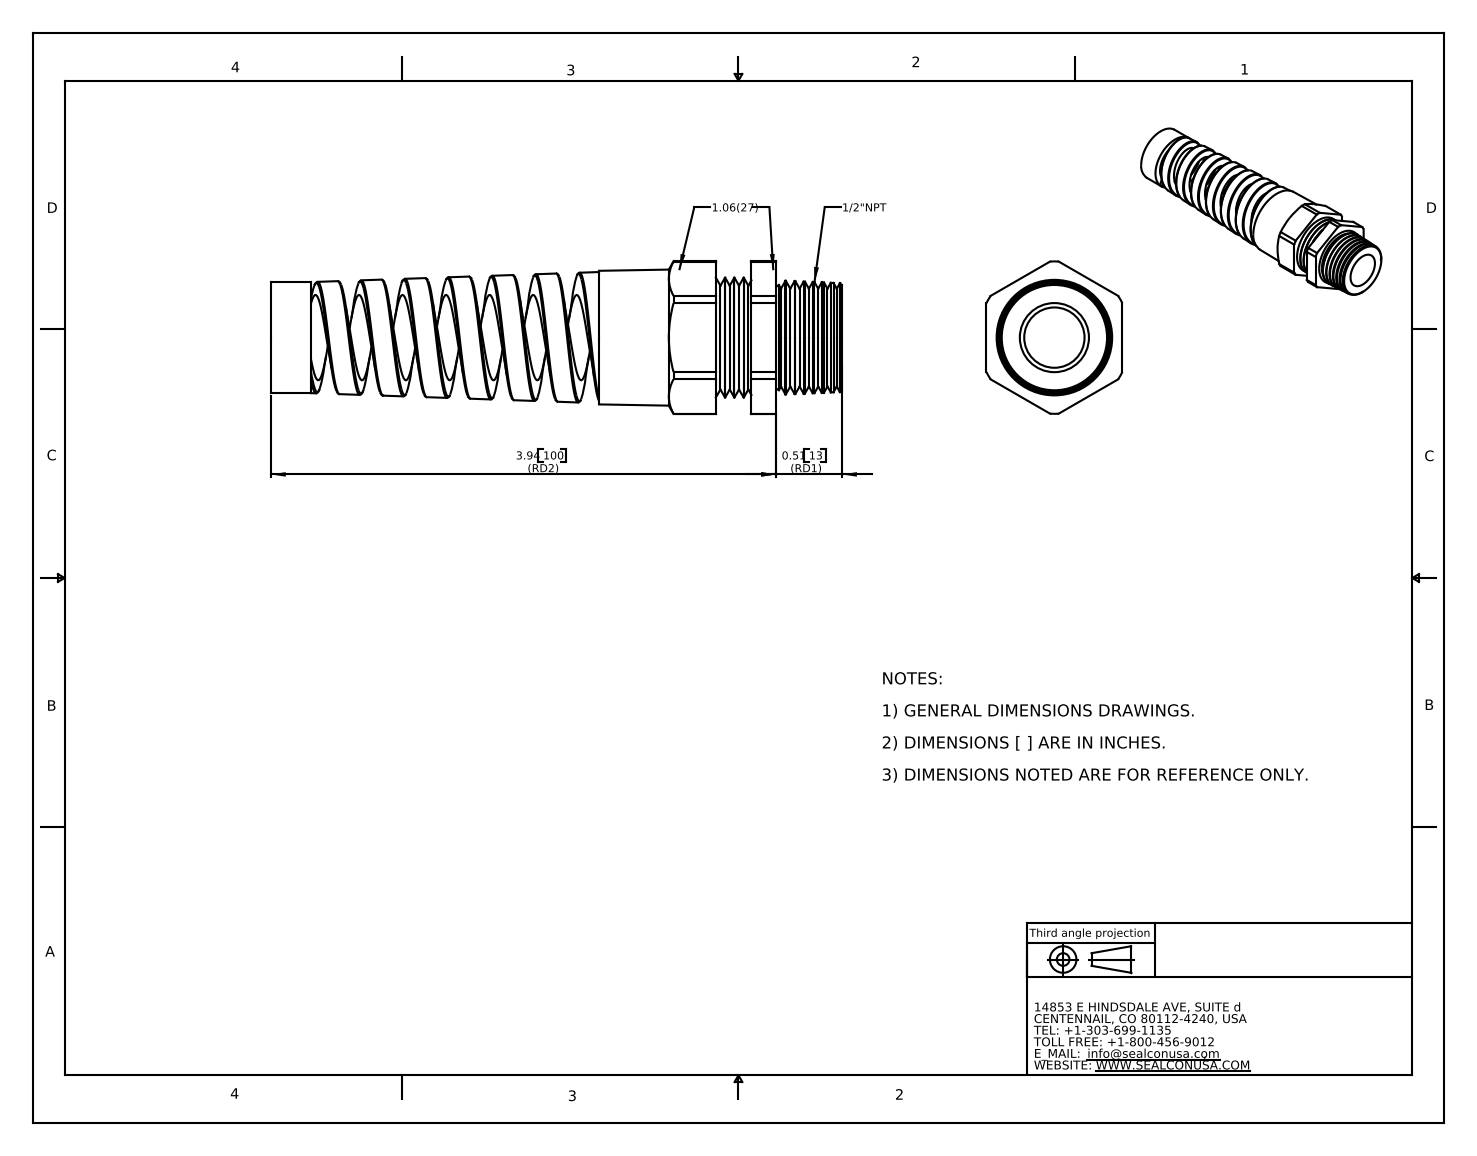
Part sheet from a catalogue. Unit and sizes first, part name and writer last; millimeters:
Units: millimetres
Overall size (bounding box): 113 × 30.1 × 26.9
Round holes (diameter × count): ⌀11.9 ×1, ⌀16.9 ×1
Round bosses / shafts (diameter × count): ⌀23.7 ×1, ⌀22 ×1
Partial cylindrical surfaces — rounded edges, fillets, slot ends (radius × count): R15.1 ×1
Main face-to-face distances: 26.9, 35.1, 48, 13, 23.1, 12, 24.9, 30.1, 7, 4.9
Volume: 26 140 mm³ · Surface area: 16 230 mm²
Bodies: 1 solid, 153 faces (19 planar, 39 cylindrical, 95 other)
Part name (STEP PRODUCT): CF16NR-BK
STEP written by: SolidWorks 2007 (CONFIG_CONTROL_DESIGN)
